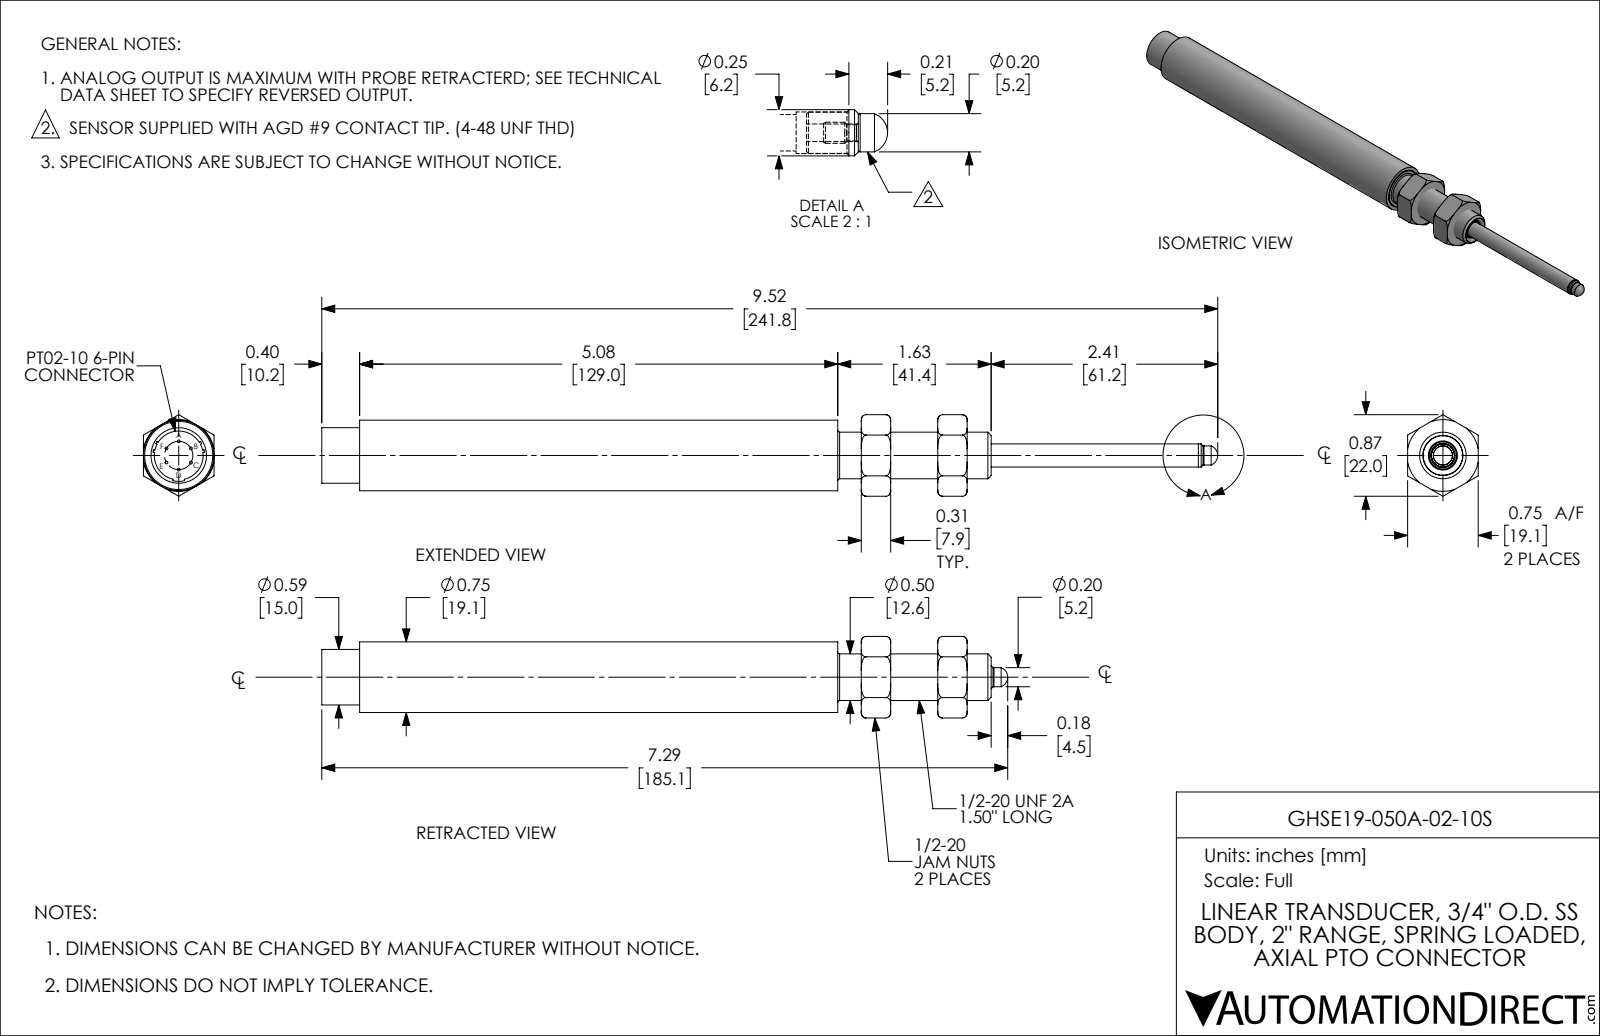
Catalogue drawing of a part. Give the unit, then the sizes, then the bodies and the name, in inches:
Units: inches
Overall size (bounding box): 7.288 × 0.866 × 0.75
Round holes (diameter × count): ⌀0.093 ×1, ⌀0.156 ×1, ⌀0.193 ×1, ⌀0.221 ×1, ⌀0.249 ×1, ⌀0.302 ×1, ⌀0.31 ×1, ⌀0.453 ×1, ⌀0.52 ×1, ⌀0.62 ×1, ⌀0.625 ×1, ⌀0.65 ×1
Round bosses / shafts (diameter × count): ⌀0.03 ×6, ⌀0.75 ×1, ⌀0.725 ×1, ⌀0.672 ×1, ⌀0.624 ×1, ⌀0.59 ×1, ⌀0.495 ×1, ⌀0.375 ×1
Partial cylindrical surfaces — rounded edges, fillets, slot ends (radius × count): R0.011 ×2, R0.04 ×2, R0.133 ×1, R0.156 ×1, R0.275 ×1
Main face-to-face distances: 0.813, 0.313, 0.75, 1.125, 0.5, 0.75, 5.352, 5.665, 6.165, 6.477
Volume: 1.442 in³ · Surface area: 45.48 in²
Bodies: 11 solids, 187 faces (77 planar, 65 cylindrical, 45 other)
Part name (STEP PRODUCT): GHSE19-050A-02-10S_retracted
STEP written by: SolidWorks 2019 (AUTOMOTIVE_DESIGN)
